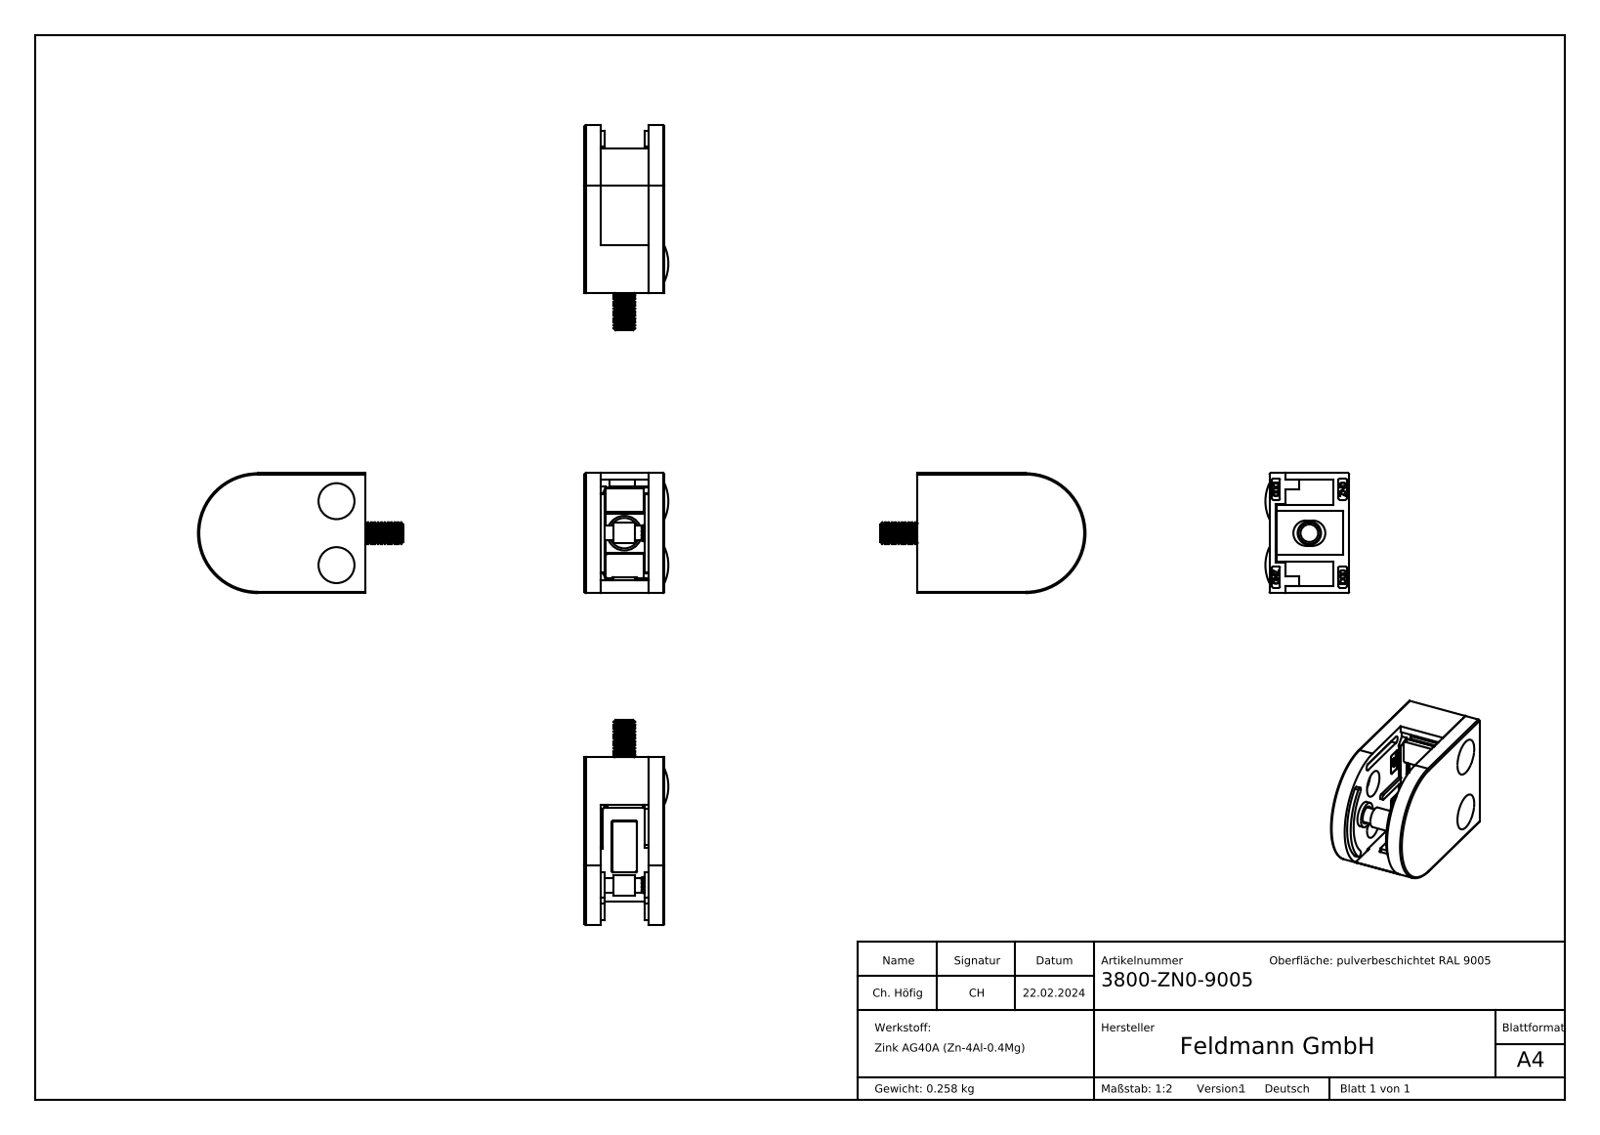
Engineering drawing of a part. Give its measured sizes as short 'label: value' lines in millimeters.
name: socket head cap screw_din_DIN 912 M8 x 20 --- 20S; 38xx-XXX Teil2_3800-ZN0-9005; 38-Stift Teil1_38-STIFT Teil1; 38-Gummi_38-GUMMI (+8 more)
written by: SolidWorks 2018 (CONFIG_CONTROL_DESIGN)
unit: mm
bodies: 13 solids, 1869 faces (977 planar, 153 cylindrical, 739 other)
size: 77 × 45 × 31.5
volume: 42 368 mm³; area: 26 975 mm²
holes: 2× ⌀2, 2× ⌀5, 2× ⌀6.4, 2× ⌀10, 2× ⌀12.2, 1× ⌀5.6, 1× ⌀6.7
bosses: 2× ⌀11.57, 2× ⌀6, 1× ⌀13, 1× ⌀9.5, 1× ⌀8, 1× ⌀7.6
rounds: 56× R0.5, 4× R1, 4× R1.35, 2× R1.2, 2× R4.75, 1× R3, 1× R18.1, 1× R20.5
face distances: 6, 24, 30, 18, 2, 2.5, 4, 3.5, 0.5, 45
hole spacings: 12.04, 29.15, 35.81, 38.9, 18, 24
